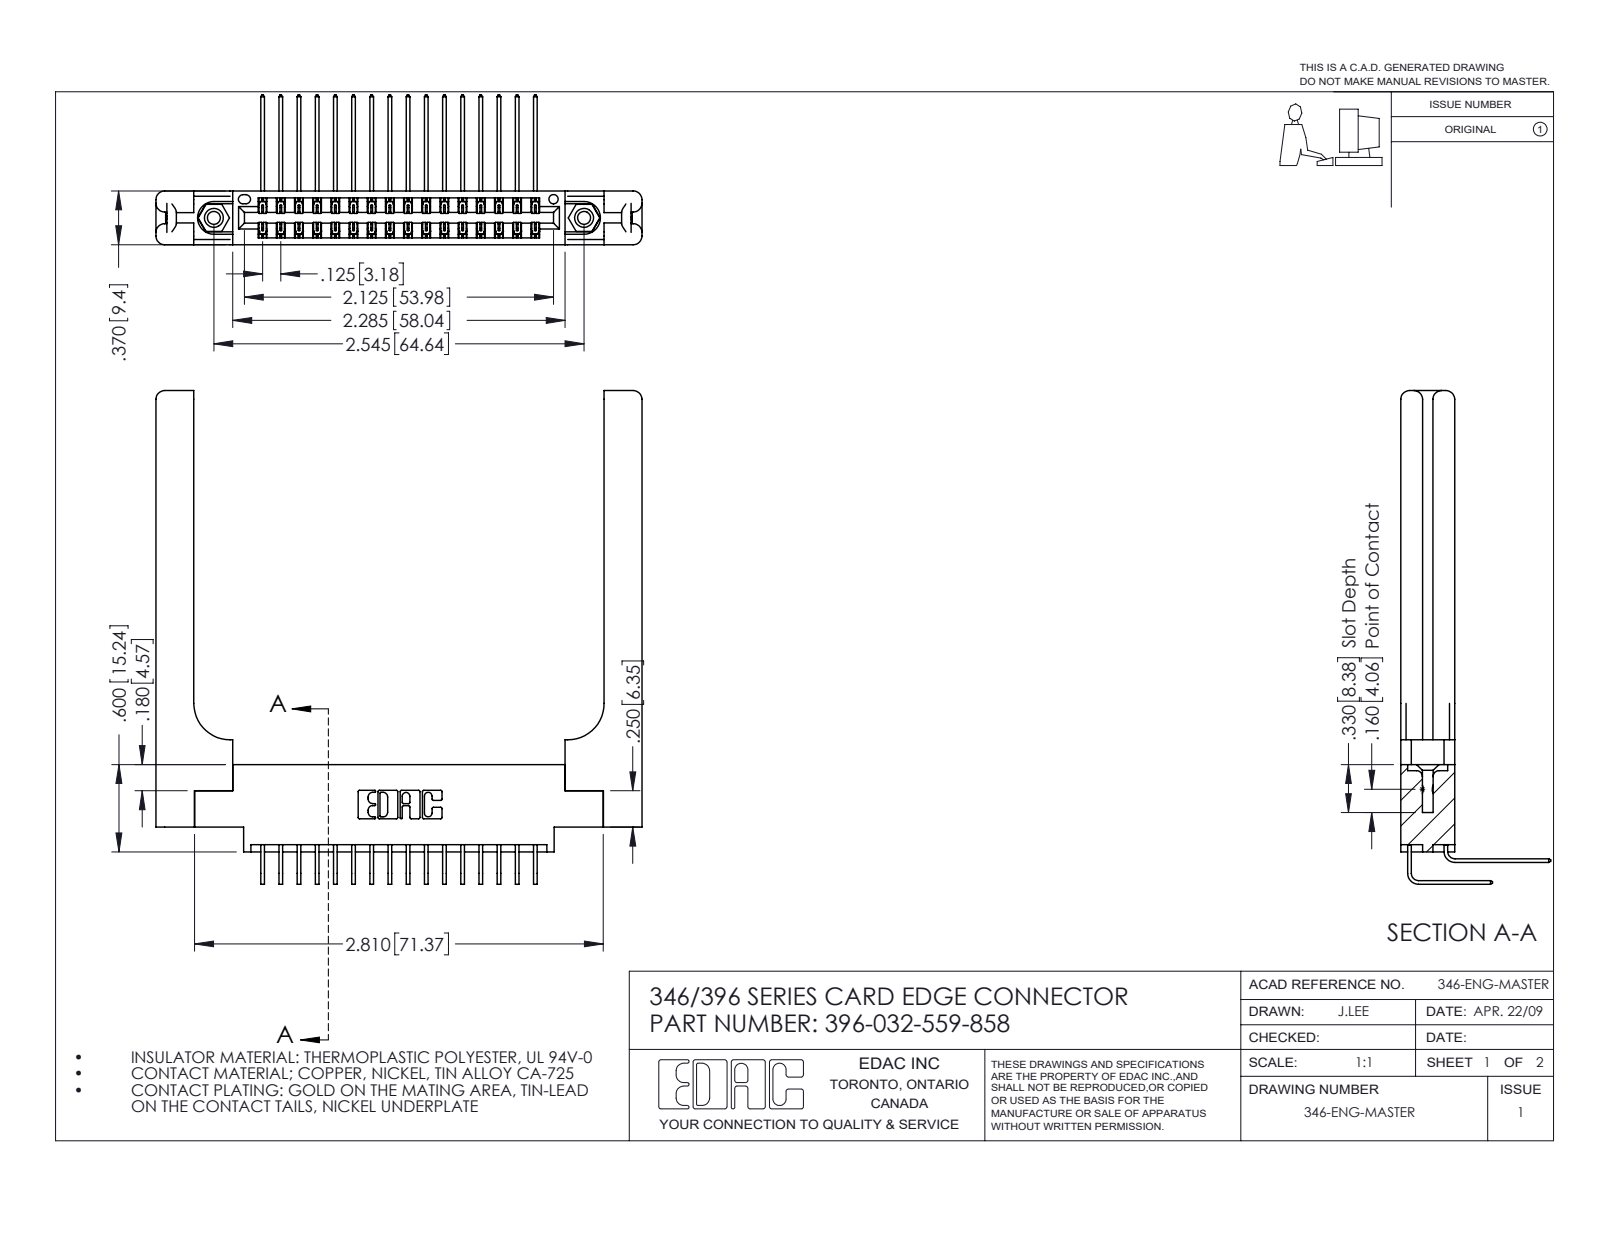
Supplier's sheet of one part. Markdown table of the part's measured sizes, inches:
| quantity | value |
| --- | --- |
| part name | 345-292-001_558 559 Tail - 1; 345-292-001_559 Tail - 2; 346-220-058_345-220-058; 396-032-559-858 (+2 more) |
| STEP written by | SolidWorks 2016 (CONFIG_CONTROL_DESIGN) |
| units | inches |
| bodies | 37 solids, 2110 faces (1412 planar, 638 cylindrical, 60 other) |
| overall size | 3.393 × 3.341 × 1.03 |
| volume | 0.952 in³ |
| surface area | 25.99 in² |
| round holes (diameter × count) | 0.089 × 2, 0.125 × 2, 0.156 × 2, 0.064 × 1 |
| round bosses / shafts (diameter × count) | 0.155 × 2 |
| partial cylindrical surfaces (radius × count) | 0.006 × 48, 0.01 × 22, 0.06 × 16, 0.007 × 6, 0.031 × 6, 0.026 × 3, 0.014 × 2, 0.022 × 2 |
| main face-to-face distances | 0.37, 0.072, 0.15, 0.048, 0.148, 0.322, 0.025, 0.25, 0.22, 0.102 |
| hole center spacings | 0.246, 2.338, 2.545 |
